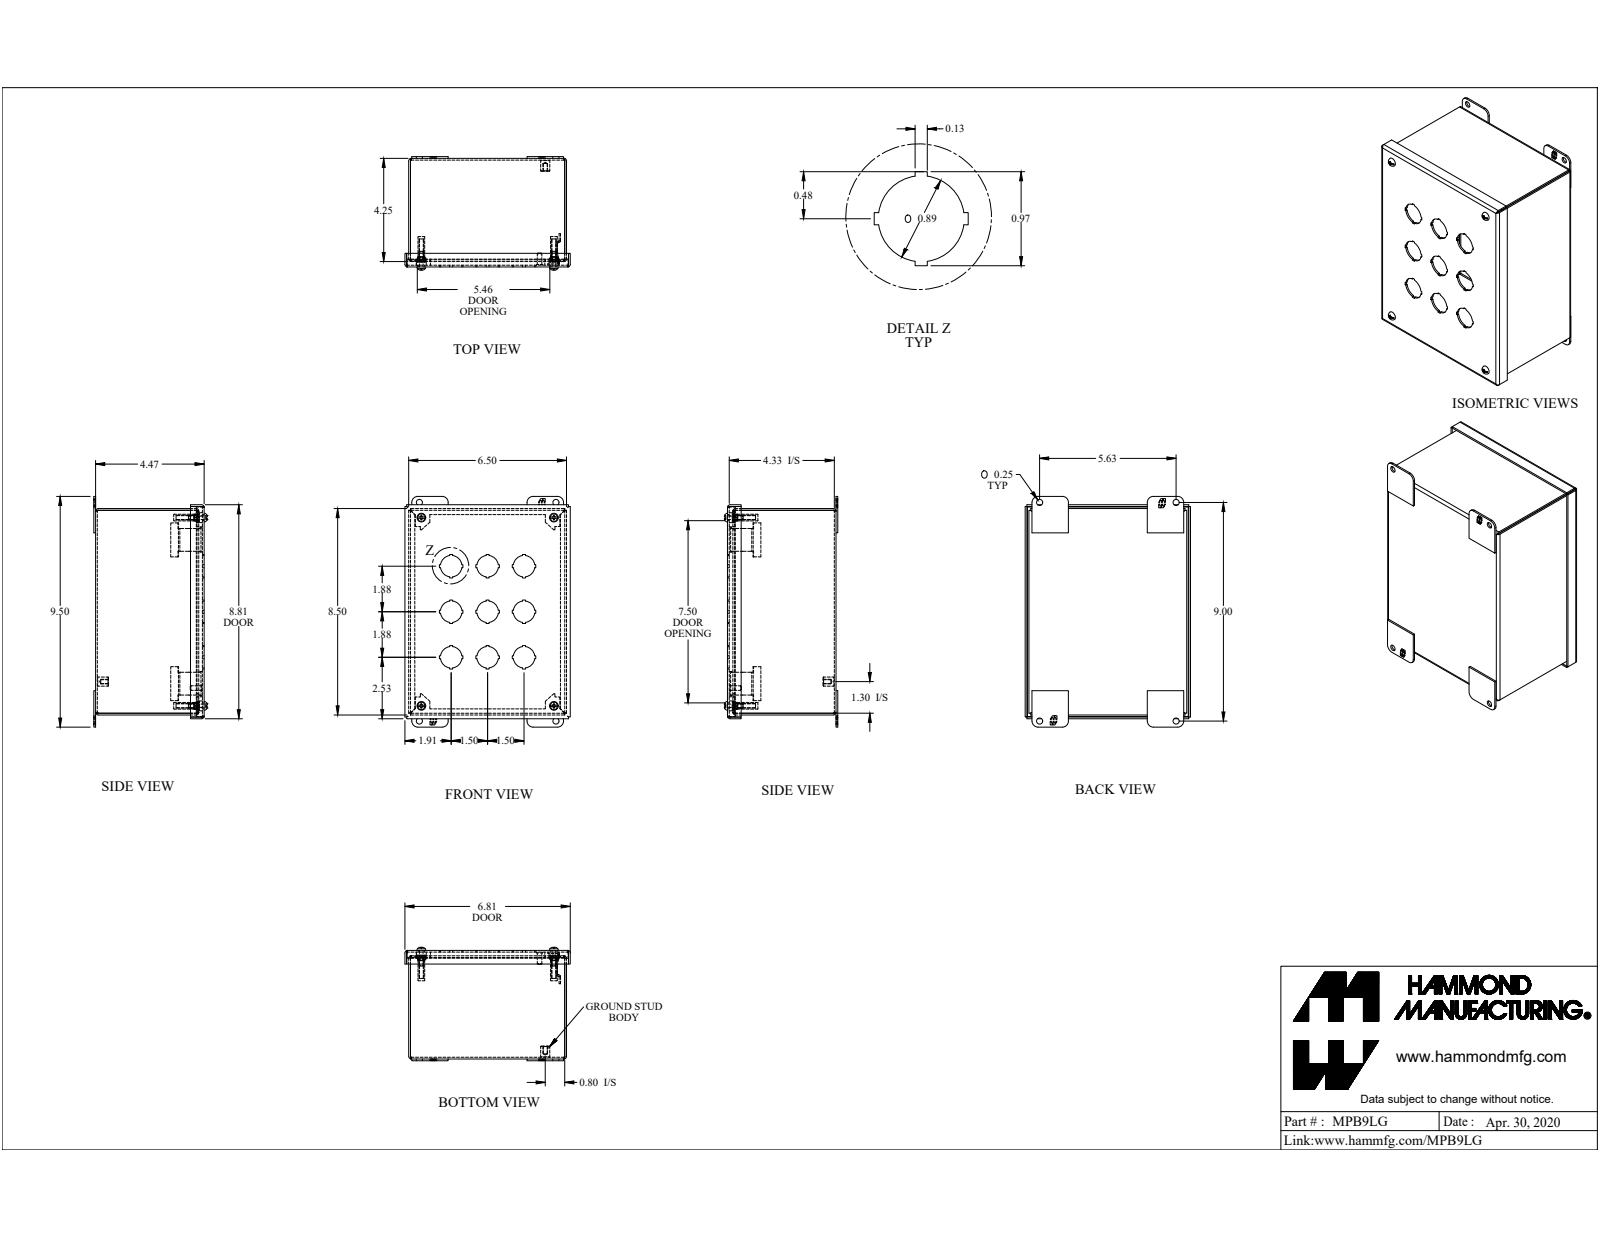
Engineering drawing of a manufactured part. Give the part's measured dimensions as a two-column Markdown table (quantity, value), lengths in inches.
| quantity | value |
| --- | --- |
| part name | MPB9LG |
| STEP written by | SolidWorks 2019 (AUTOMOTIVE_DESIGN) |
| units | inches |
| bodies | 23 solids, 795 faces (607 planar, 152 cylindrical, 36 other) |
| overall size | 9.5 × 6.813 × 4.671 |
| volume | 22.03 in³ |
| surface area | 588.2 in² |
| round holes (diameter × count) | 0.886 × 9, 0.25 × 8, 0.159 × 4, 0.406 × 4, 0.156 × 1 |
| round bosses / shafts (diameter × count) | 0.39 × 4, 0.275 × 4, 0.19 × 4, 0.148 × 4, 0.375 × 1, 0.25 × 1, 0.188 × 1 |
| partial cylindrical surfaces (radius × count) | 0.036 × 12, 0.108 × 12, 0.25 × 8, 0.029 × 4, 0.086 × 4, 0.16 × 4, 0.171 × 4 |
| main face-to-face distances | 0.072, 4.4, 6.428, 4.472, 4.328, 8.428, 6.5, 6.356, 8.5, 8.356 |
| hole center spacings | 2.401, 5.461, 5.578, 1.5, 5.737, 0.63, 0.631, 3.538 |
